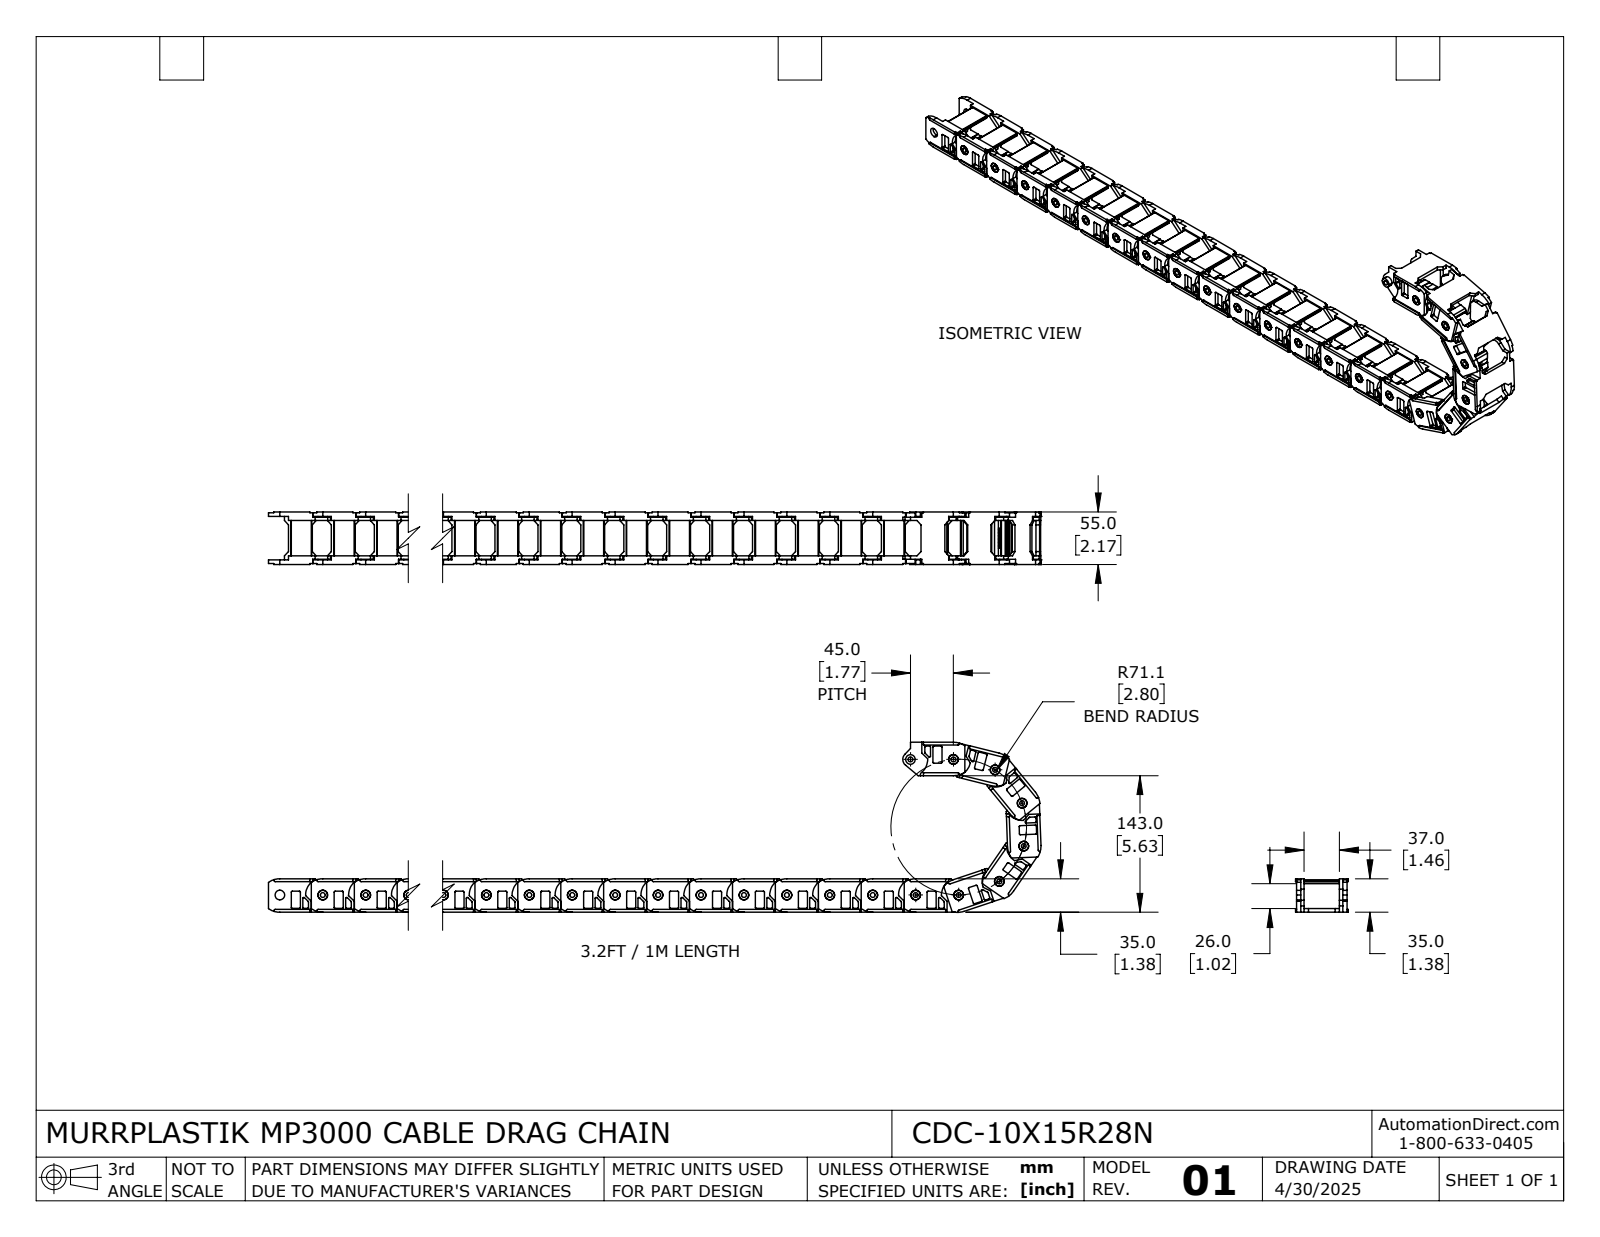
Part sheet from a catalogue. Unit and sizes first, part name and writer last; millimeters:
Units: millimetres
Overall size (bounding box): 817.98 × 178.14 × 55
Round holes (diameter × count): ⌀5.1 ×22, ⌀10.1 ×22
Round bosses / shafts (diameter × count): ⌀10 ×22
Partial cylindrical surfaces — rounded edges, fillets, slot ends (radius × count): R1 ×176, R0.5 ×88, R1.5 ×44, R2 ×44, R21 ×44, R2.8 ×22, R8 ×22, R18 ×22
Main face-to-face distances: 45, 8, 4, 3.7, 49.3, 4.3, 41.3, 37, 3.5, 0.8
Hole centre spacings: 44.98, 89.96, 45, 134.94, 179.92, 44.96, 224.9, 89.98
Volume: 587 391 mm³ · Surface area: 349 280 mm²
Bodies: 22 solids, 3696 faces (2596 planar, 1100 cylindrical, 0 other)
Part name (STEP PRODUCT): CDC-10X15R28N
STEP written by: SolidWorks 2024 (AUTOMOTIVE_DESIGN)
